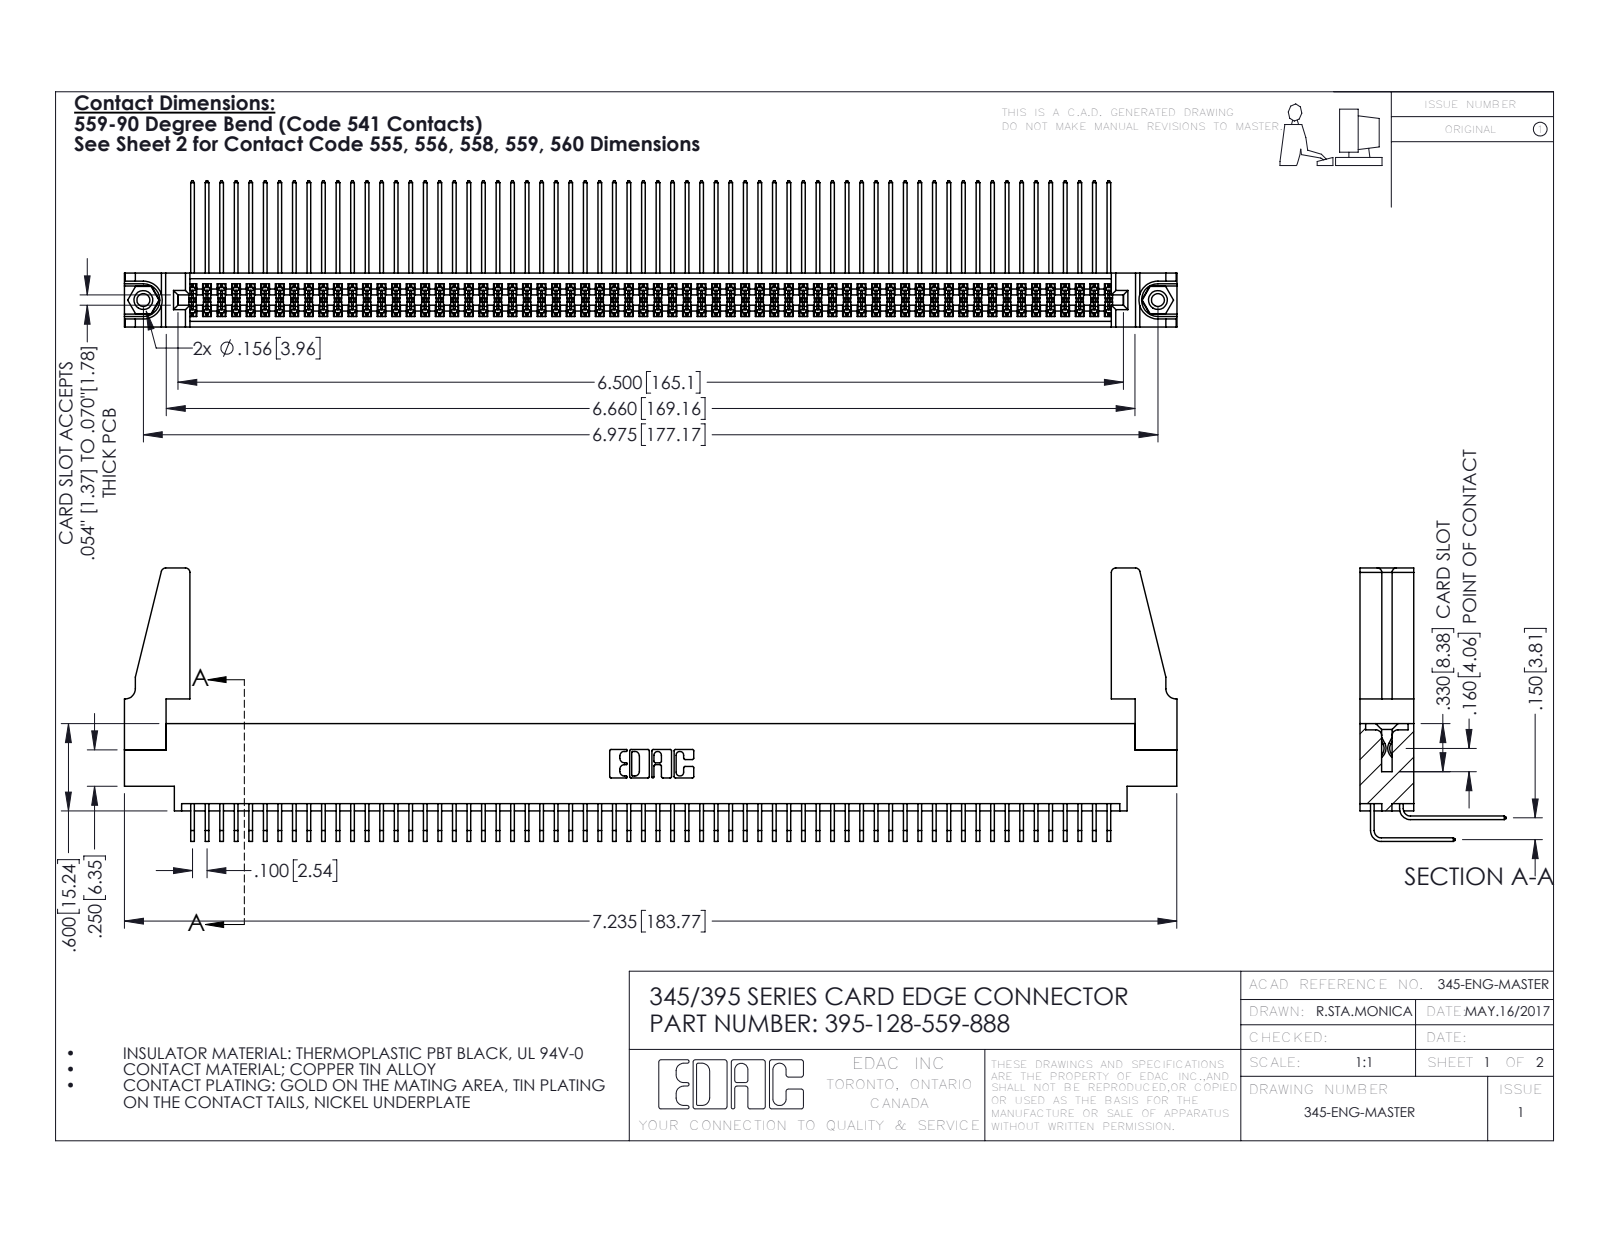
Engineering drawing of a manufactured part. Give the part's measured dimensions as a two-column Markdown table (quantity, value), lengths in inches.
| quantity | value |
| --- | --- |
| part name | 345-292-001_559 Tail - 2; 345 Part_0.170 Offset - 0.156 Dia-TH; 345-292-001_558 559 Tail - 1; 395-128-559-888 (+2 more) |
| STEP written by | SolidWorks 2016 (CONFIG_CONTROL_DESIGN) |
| units | inches |
| bodies | 133 solids, 6910 faces (4636 planar, 2258 cylindrical, 16 other) |
| overall size | 7.236 × 1.879 × 1.005 |
| volume | 1.339 in³ |
| surface area | 53.91 in² |
| round holes (diameter × count) | 0.089 × 2, 0.125 × 2, 0.156 × 2, 0.064 × 1 |
| round bosses / shafts (diameter × count) | 0.155 × 2 |
| partial cylindrical surfaces (radius × count) | 0.006 × 192, 0.01 × 22, 0.03 × 8, 0.007 × 6, 0.031 × 6, 0.026 × 3, 0.014 × 2, 0.019 × 2 |
| main face-to-face distances | 0.072, 0.298, 0.37, 0.098, 0.272, 0.025, 0.2, 0.225, 0.15, 0.175 |
| hole center spacings | 0.27, 6.739, 6.975 |
